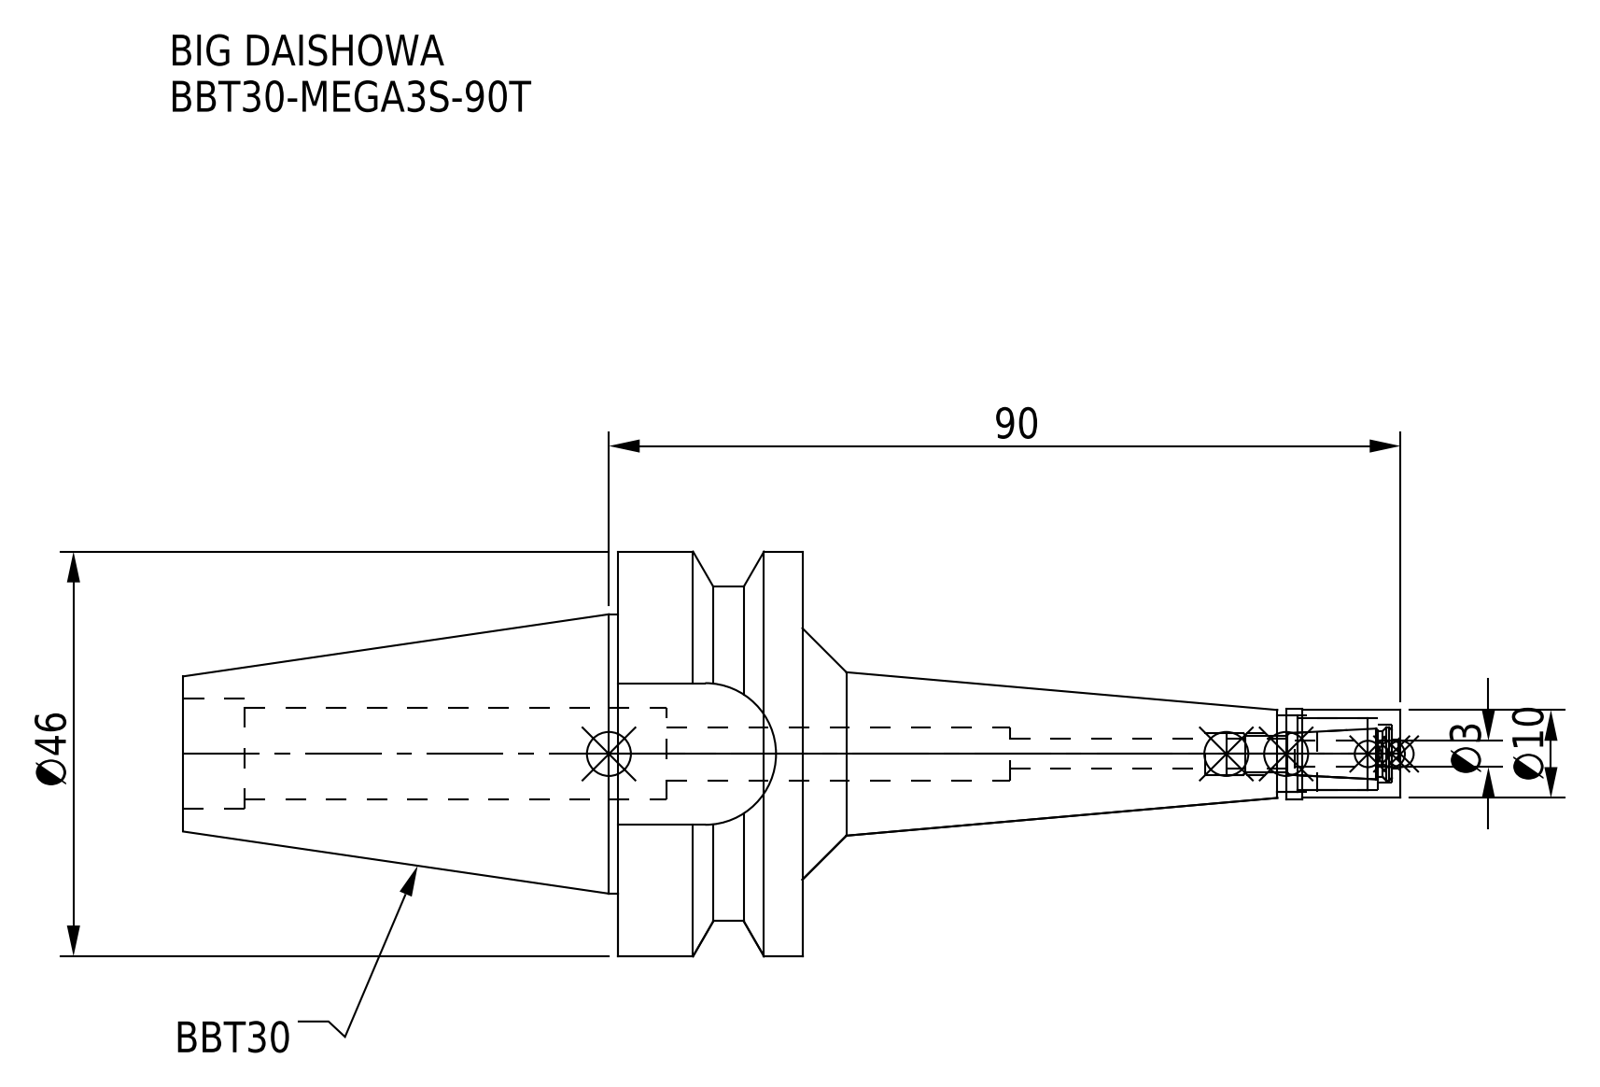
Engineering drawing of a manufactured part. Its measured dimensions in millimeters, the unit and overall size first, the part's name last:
Units: millimetres
Overall size (bounding box): 138.4 × 46 × 46
Round holes (diameter × count): ⌀3.3 ×1, ⌀3.4 ×1, ⌀4.7 ×1, ⌀6 ×1, ⌀6.6 ×1, ⌀8.2 ×1, ⌀8.7 ×1, ⌀10.4 ×1, ⌀12.5 ×1
Round bosses / shafts (diameter × count): ⌀46 ×1, ⌀31.75 ×1, ⌀10.3 ×1, ⌀10 ×1
Partial cylindrical surfaces — rounded edges, fillets, slot ends (radius × count): R8.05 ×1, R19 ×1
Main face-to-face distances: 21, 32.6, 70.4, 49.4, 16.1, 55, 68, 89, 138.4, 83.4
Volume: 58 492 mm³ · Surface area: 16 619 mm²
Bodies: 2 solids, 74 faces (22 planar, 38 cylindrical, 14 other)
Part name (STEP PRODUCT): BBT30-MEGA3S-90T_1.stp; BBT30-MEGA3S-90T.stp; BBT30-MEGA3S-90T; MGN3S_1.stp (+3 more)
STEP written by: SolidWorks 2019 (CONFIG_CONTROL_DESIGN)
